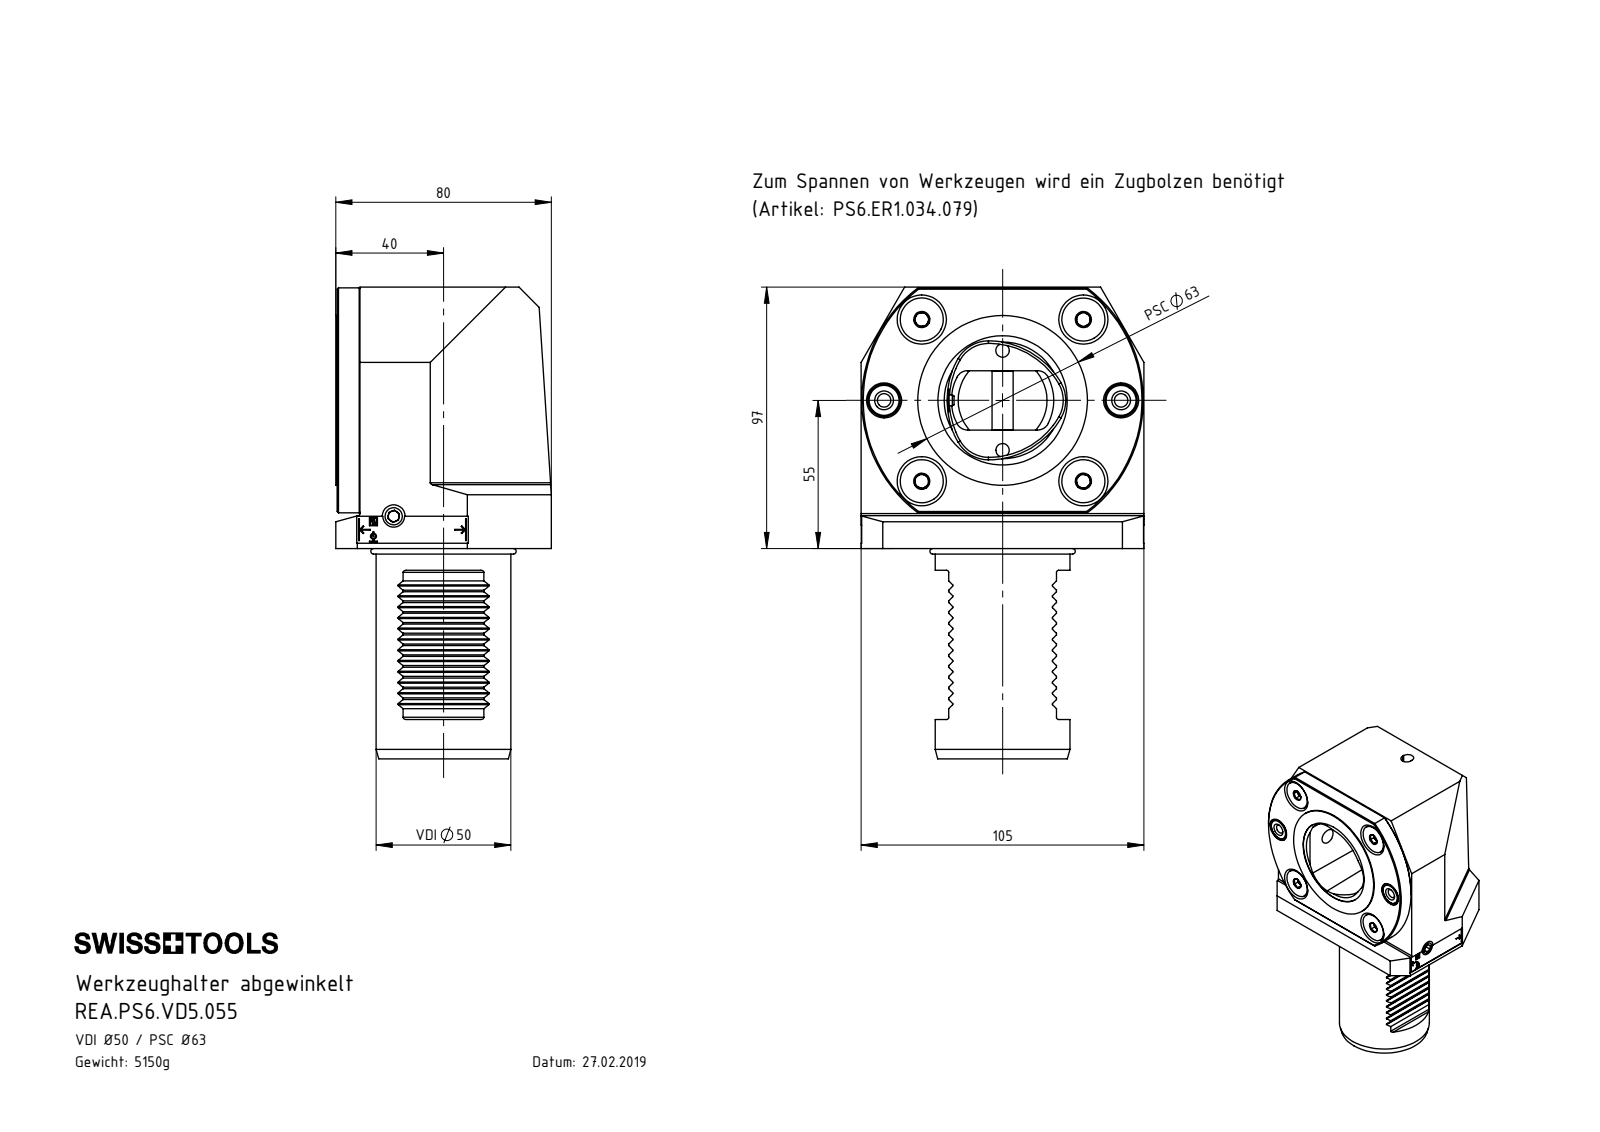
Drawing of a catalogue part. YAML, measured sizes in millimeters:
part_name: "ISO 8734 - 6 x 14_PreviewCfg; U63-PS6.ER1.058_A; REA.PS6.VD5.055; DIN 6325_ø5x12_2x6 (+8 more)"
step_written_by: "SolidWorks 2022 (AUTOMOTIVE_DESIGN)"
units: millimeters
bodies: {solids: 27, faces: 1004, planar: 408, cylindrical: 258, other: 338}
overall_size: [175, 105, 80]
volume: 696000
surface_area: 159588
round_holes:
  - {diameter: 6.8, count: 7}
  - {diameter: 5, count: 5}
  - {diameter: 9, count: 5}
  - {diameter: 4, count: 3}
  - {diameter: 4.2, count: 2}
  - {diameter: 5.5, count: 2}
  - {diameter: 12, count: 2}
  - {diameter: 13, count: 2}
  - {diameter: 15, count: 2}
  - {diameter: 2.4, count: 1}
  - {diameter: 2.5, count: 1}
  - {diameter: 6, count: 1}
round_bosses_or_shafts:
  - {diameter: 8, count: 6}
  - {diameter: 16, count: 5}
  - {diameter: 8.5, count: 2}
  - {diameter: 5, count: 2}
  - {diameter: 63, count: 1}
  - {diameter: 62.7, count: 1}
  - {diameter: 59, count: 1}
  - {diameter: 58.8, count: 1}
partial_cylinders:
  - {radius: 0.3, count: 24}
  - {radius: 0.8, count: 7}
  - {radius: 0.1, count: 6}
  - {radius: 4.5, count: 4}
  - {radius: 3.25, count: 2}
  - {radius: 5, count: 2}
  - {radius: 11, count: 1}
  - {radius: 19, count: 1}
face_to_face_distances: [57, 97, 3, 8.5, 65.5, 94, 66, 27, 30, 0.5]
hole_center_spacings: [32.13, 33.11, 42.43, 47.73, 57.03, 60, 79.85, 37]
